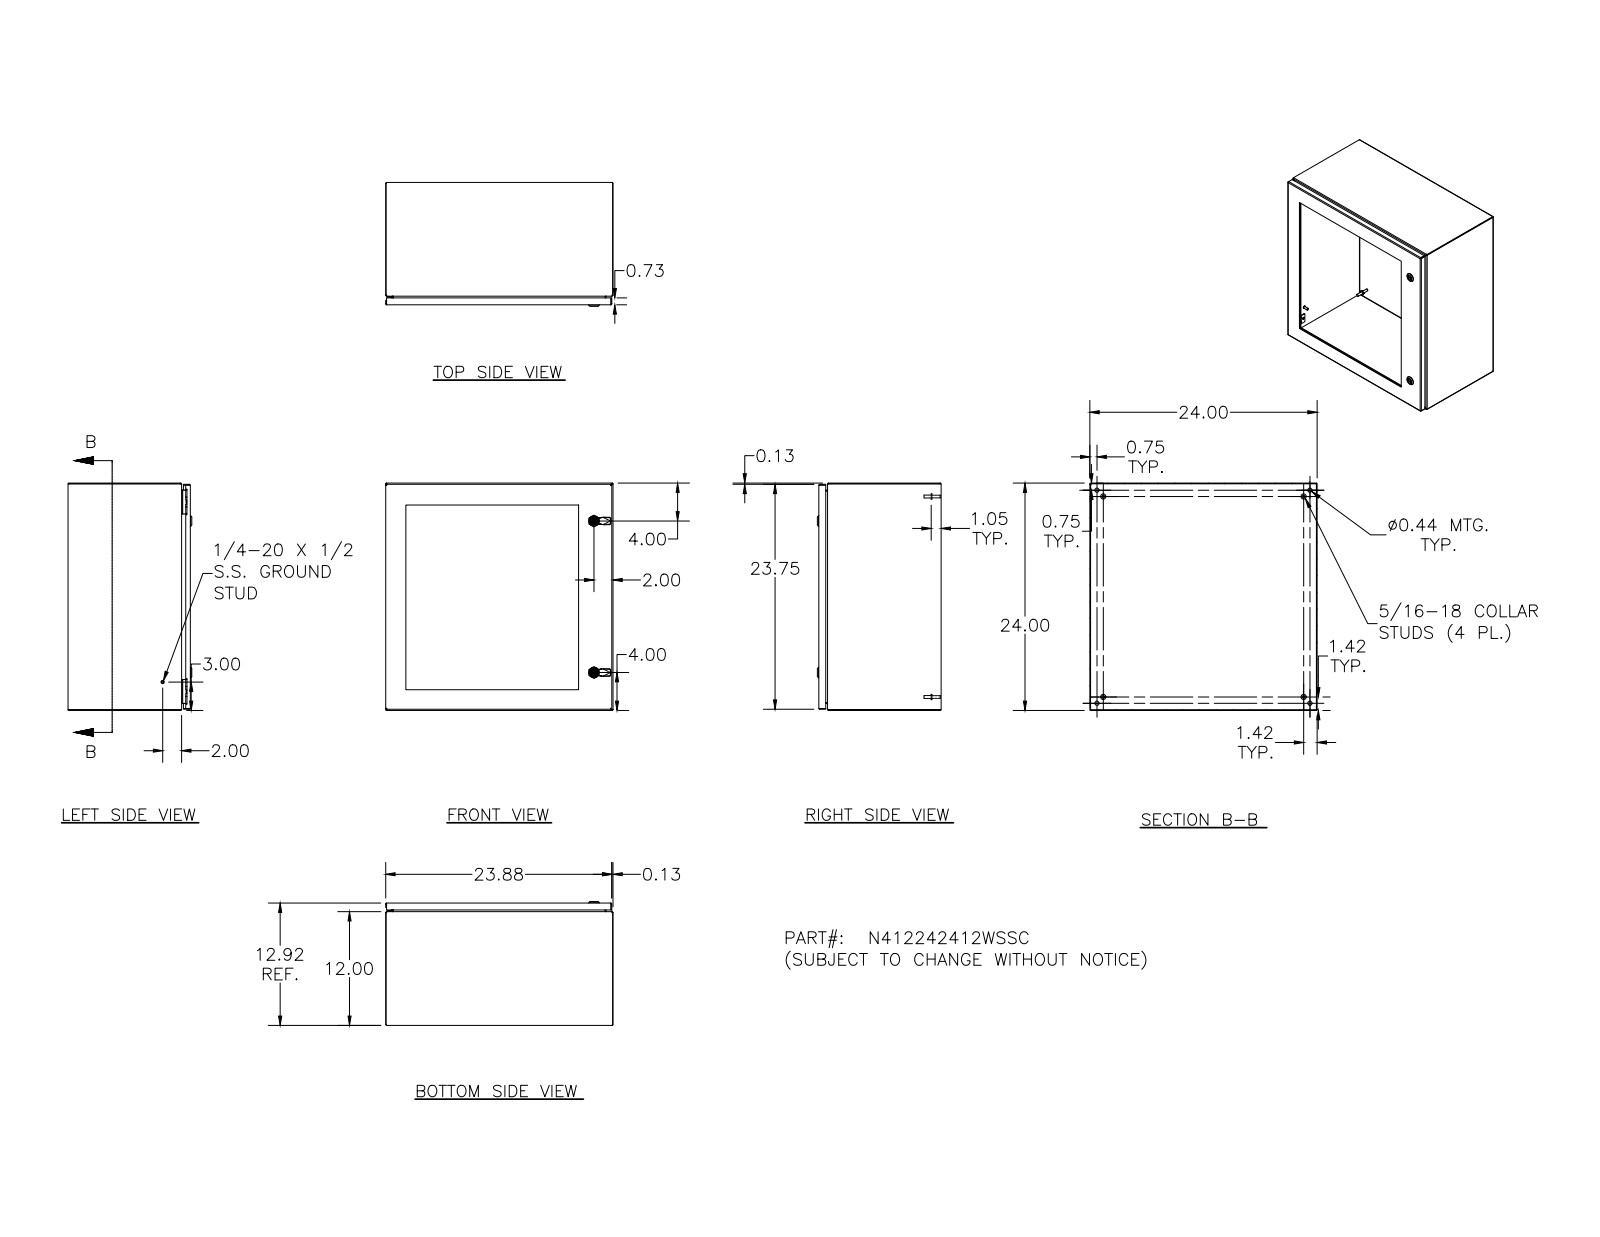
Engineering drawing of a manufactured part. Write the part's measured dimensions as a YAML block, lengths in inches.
part_name: "N412242412WSSC; N412242412WSSCBKP; N4122424WSSCLID; HFW328176 (+8 more)"
step_written_by: "Autodesk Inventor 2011 (AUTOMOTIVE_DESIGN)"
units: inches
bodies: {solids: 86, faces: 2366, planar: 973, cylindrical: 672, other: 721}
overall_size: [24, 24, 13.075]
volume: 264.3
surface_area: 5326
round_holes:
  - {diameter: 0.156, count: 22}
  - {diameter: 0.281, count: 20}
  - {diameter: 0.093, count: 4}
  - {diameter: 0.152, count: 4}
  - {diameter: 0.167, count: 4}
  - {diameter: 0.172, count: 4}
  - {diameter: 0.188, count: 4}
  - {diameter: 0.437, count: 4}
  - {diameter: 0.197, count: 2}
  - {diameter: 0.315, count: 2}
  - {diameter: 0.394, count: 2}
  - {diameter: 0.402, count: 2}
round_bosses_or_shafts:
  - {diameter: 0.19, count: 20}
  - {diameter: 0.253, count: 19}
  - {diameter: 0.25, count: 10}
  - {diameter: 0.563, count: 4}
  - {diameter: 0.36, count: 4}
  - {diameter: 0.32, count: 4}
  - {diameter: 0.3, count: 4}
  - {diameter: 0.275, count: 4}
partial_cylinders:
  - {radius: 0.031, count: 34}
  - {radius: 0.05, count: 26}
  - {radius: 0.105, count: 24}
  - {radius: 0.016, count: 18}
  - {radius: 0.125, count: 16}
  - {radius: 0.02, count: 15}
  - {radius: 0.032, count: 8}
  - {radius: 0.157, count: 8}
face_to_face_distances: [0.074, 23.926, 12.843, 12.769, 24, 23.852, 0.25, 12.593, 12.519, 12.917]
hole_center_spacings: [4, 8, 21.132, 12, 19.906, 20, 22.239, 20.75]
